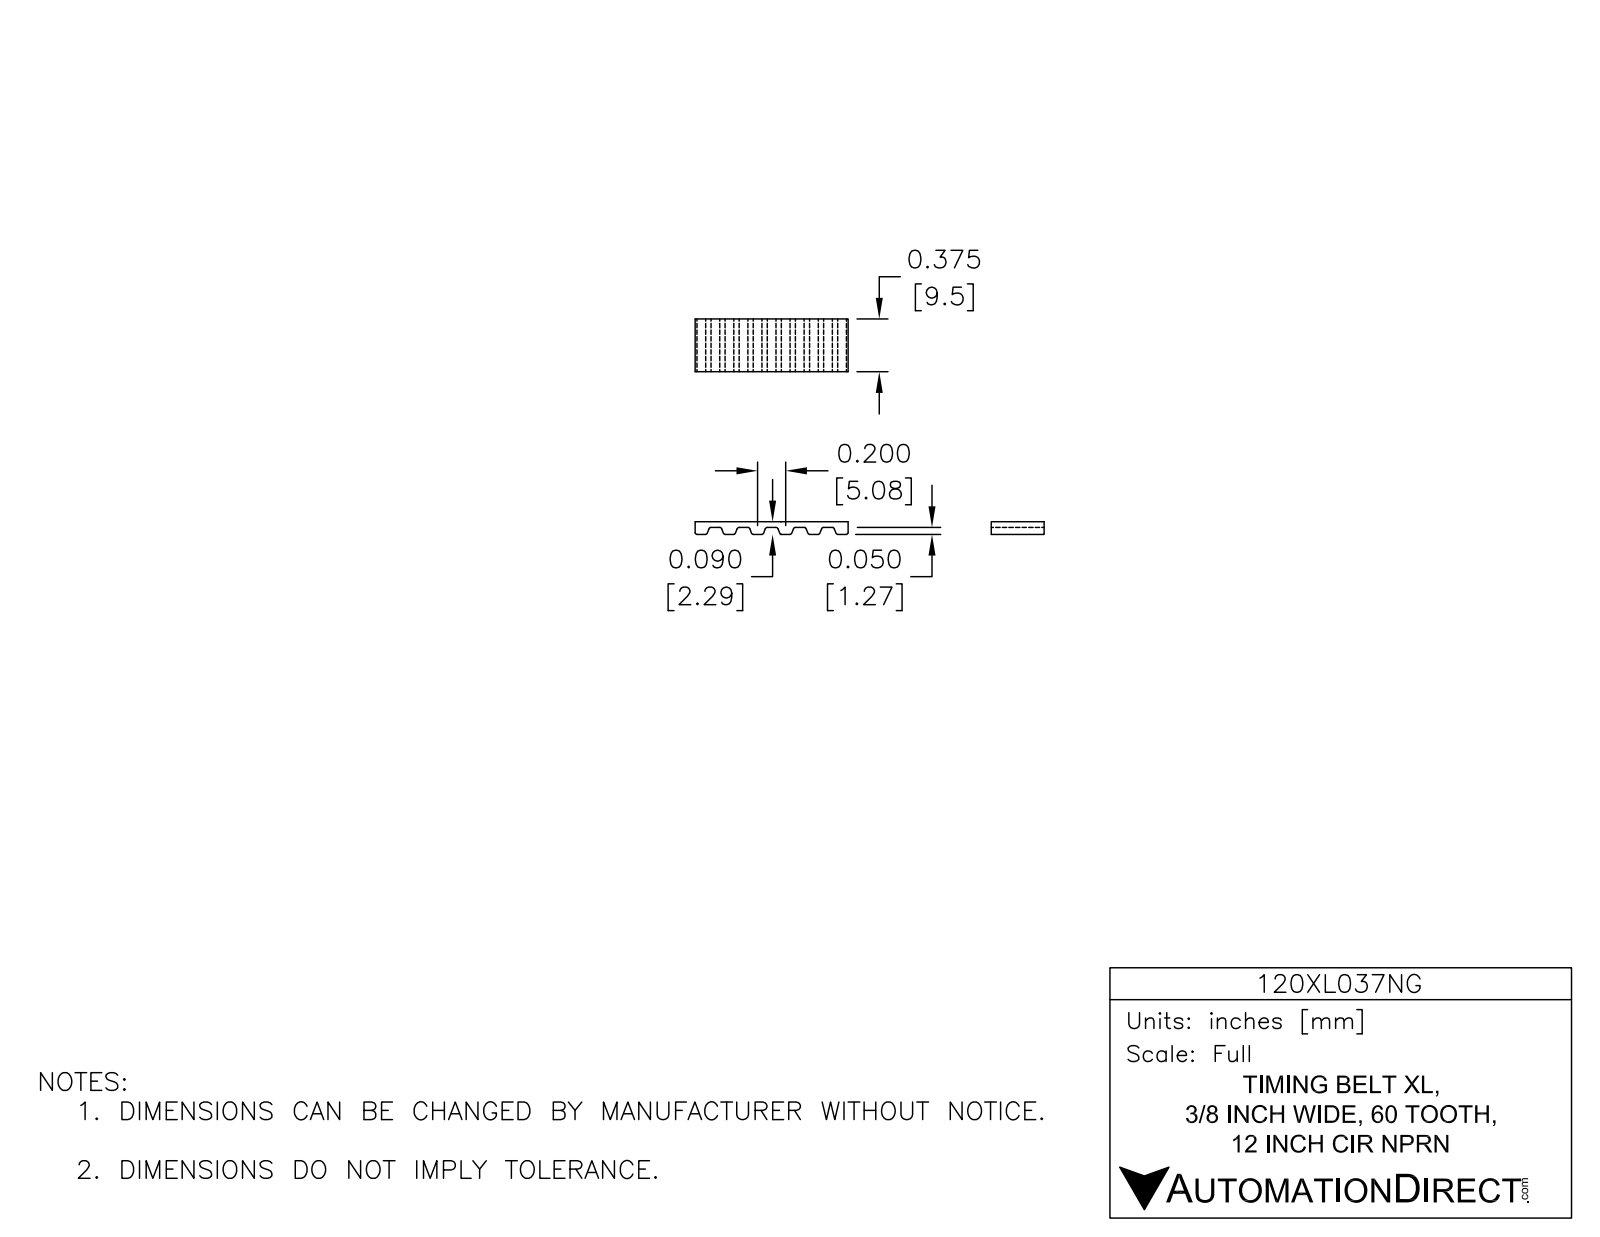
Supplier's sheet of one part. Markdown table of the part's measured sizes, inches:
| quantity | value |
| --- | --- |
| part name | 120XL037NG |
| STEP written by | SolidWorks 2014 (AUTOMOTIVE_DESIGN) |
| units | inches |
| bodies | 1 solid, 520 faces (200 planar, 320 cylindrical, 0 other) |
| overall size | 4.288 × 3 × 0.375 |
| volume | 0.244 in³ |
| surface area | 11.45 in² |
| partial cylindrical surfaces (radius × count) | 0.015 × 240, 1.46 × 2, 1.5 × 2 |
| main face-to-face distances | 0.375, 3, 0.04, 2.96, 2.92, 0.178, 0.532, 0.355, 0.983, 1.161 |
